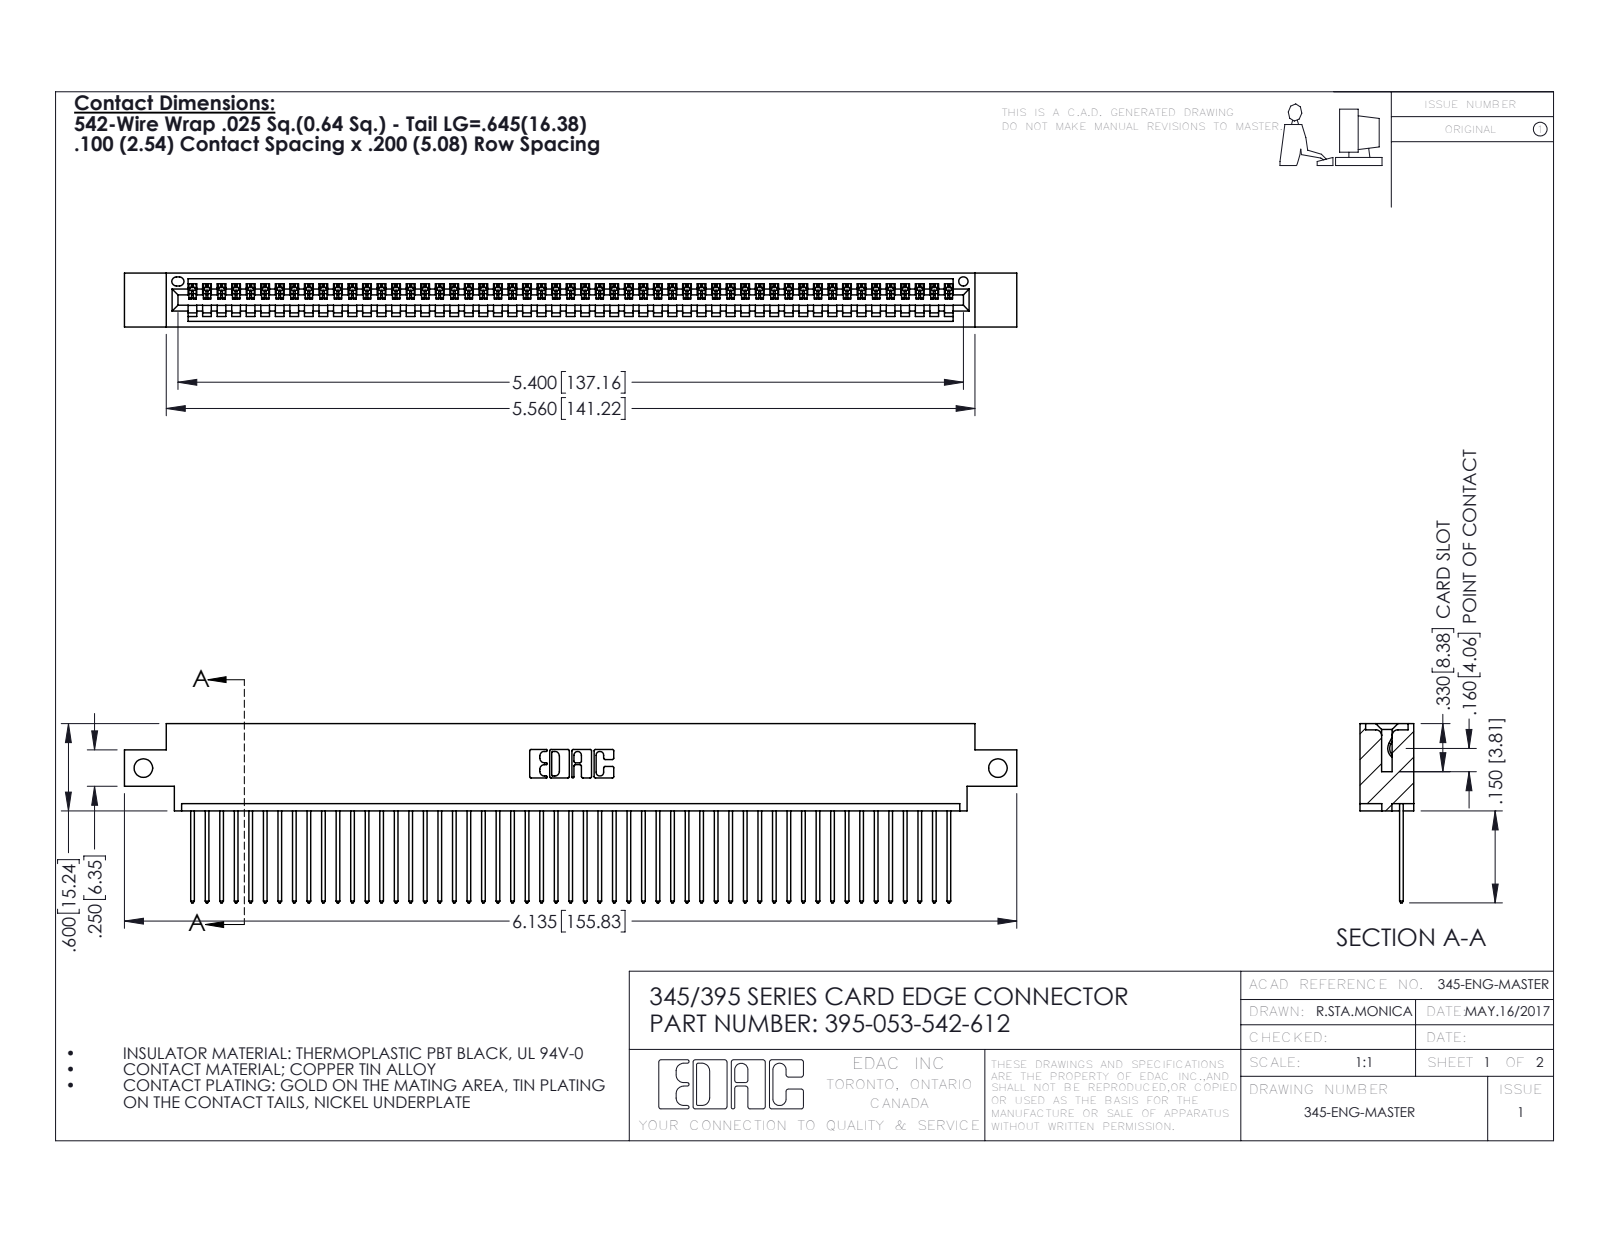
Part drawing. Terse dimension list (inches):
name: 345 Part_0.170 Offset - Side Mount; 395-053-542-612; 345-292-001_345-293-142
written by: SolidWorks 2016 (CONFIG_CONTROL_DESIGN)
unit: in
bodies: 54 solids, 3204 faces (2204 planar, 1000 cylindrical, 0 other)
size: 6.135 × 1.232 × 0.37
volume: 0.904 in³; area: 31.87 in²
holes: 2× ⌀0.128, 1× ⌀0.064
rounds: 106× R0.006, 106× R0.01, 22× R0.01, 6× R0.007, 6× R0.031, 3× R0.026, 2× R0.031, 2× R0.04
face distances: 0.072, 0.298, 0.37, 0.098, 0.272, 0.025, 0.2, 0.225, 0.175, 0.149
hole spacings: 5.875
